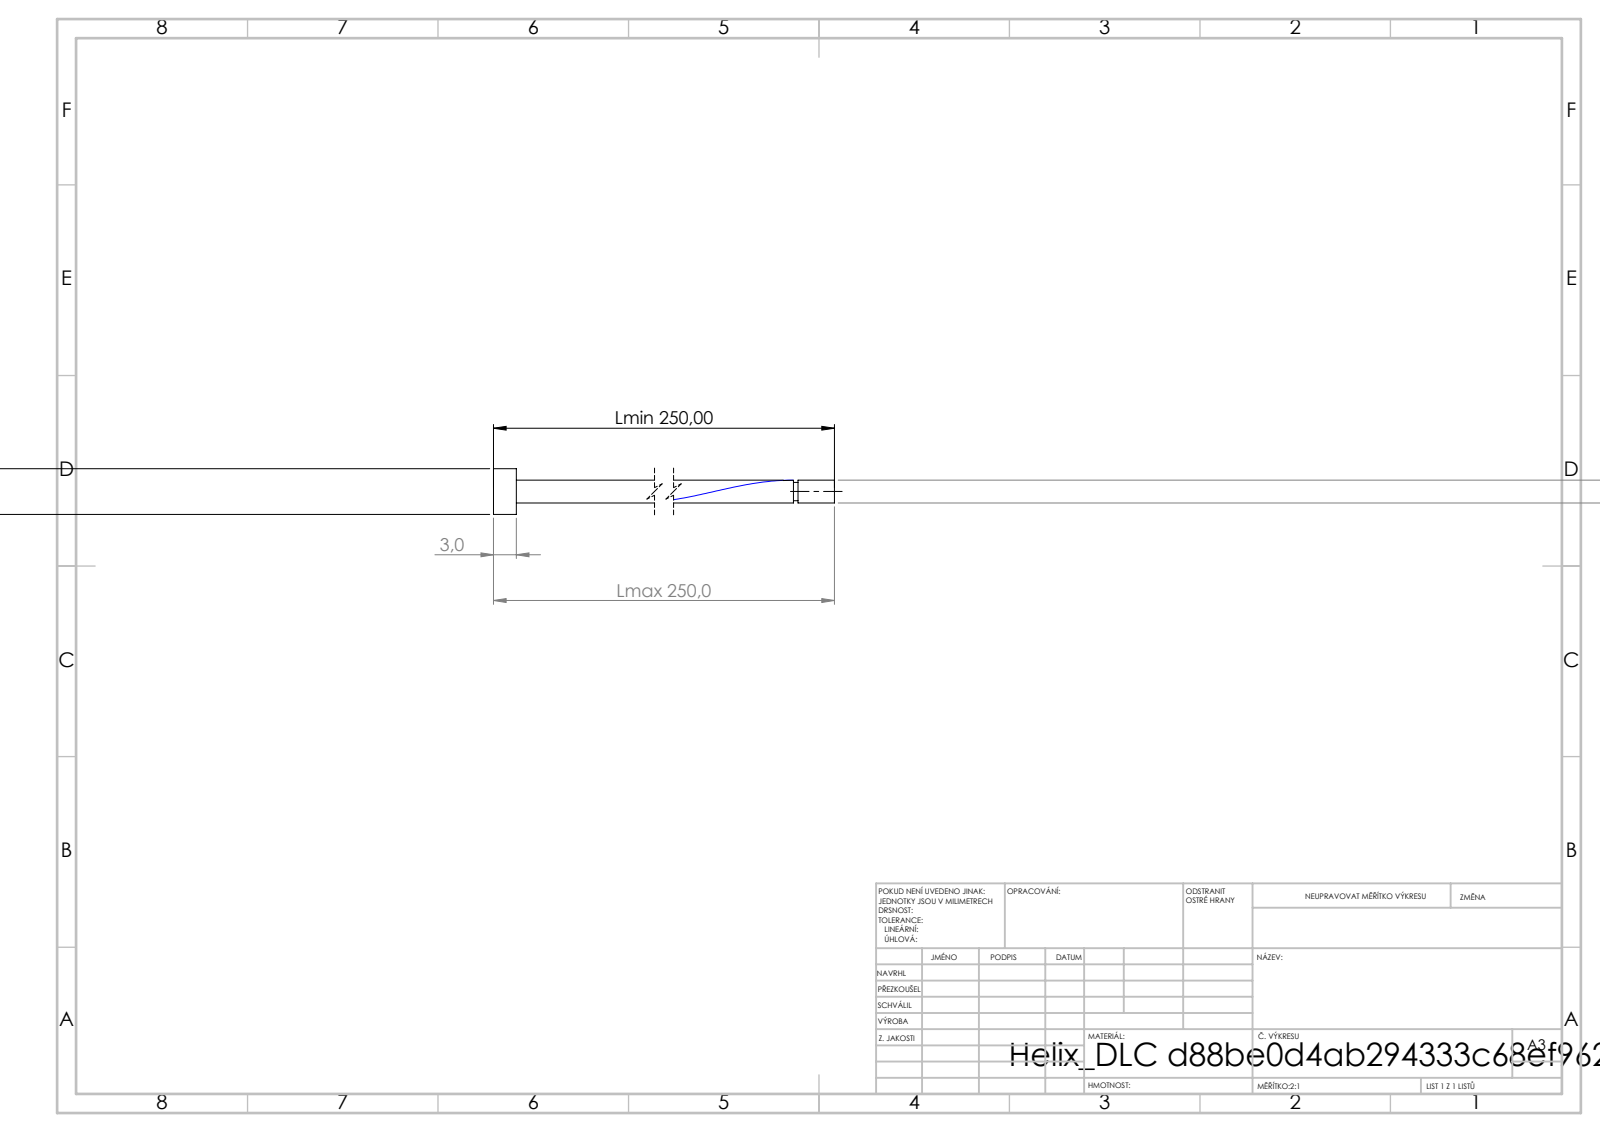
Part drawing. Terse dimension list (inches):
written by: SolidWorks 2019 (CONFIG_CONTROL_DESIGN)
unit: in
bodies: 1 solid, 16 faces (6 planar, 9 cylindrical, 1 other)
size: 9.843 × 0.236 × 0.236
volume: 0.135 in³; area: 5.065 in²
bosses: 1× ⌀0.236, 1× ⌀0.118, 1× ⌀0.094
face distances: 0.118, 9.843, 9.724, 9.654, 9.536, 0.188, 9.631, 9.513, 0.024, 0.212
